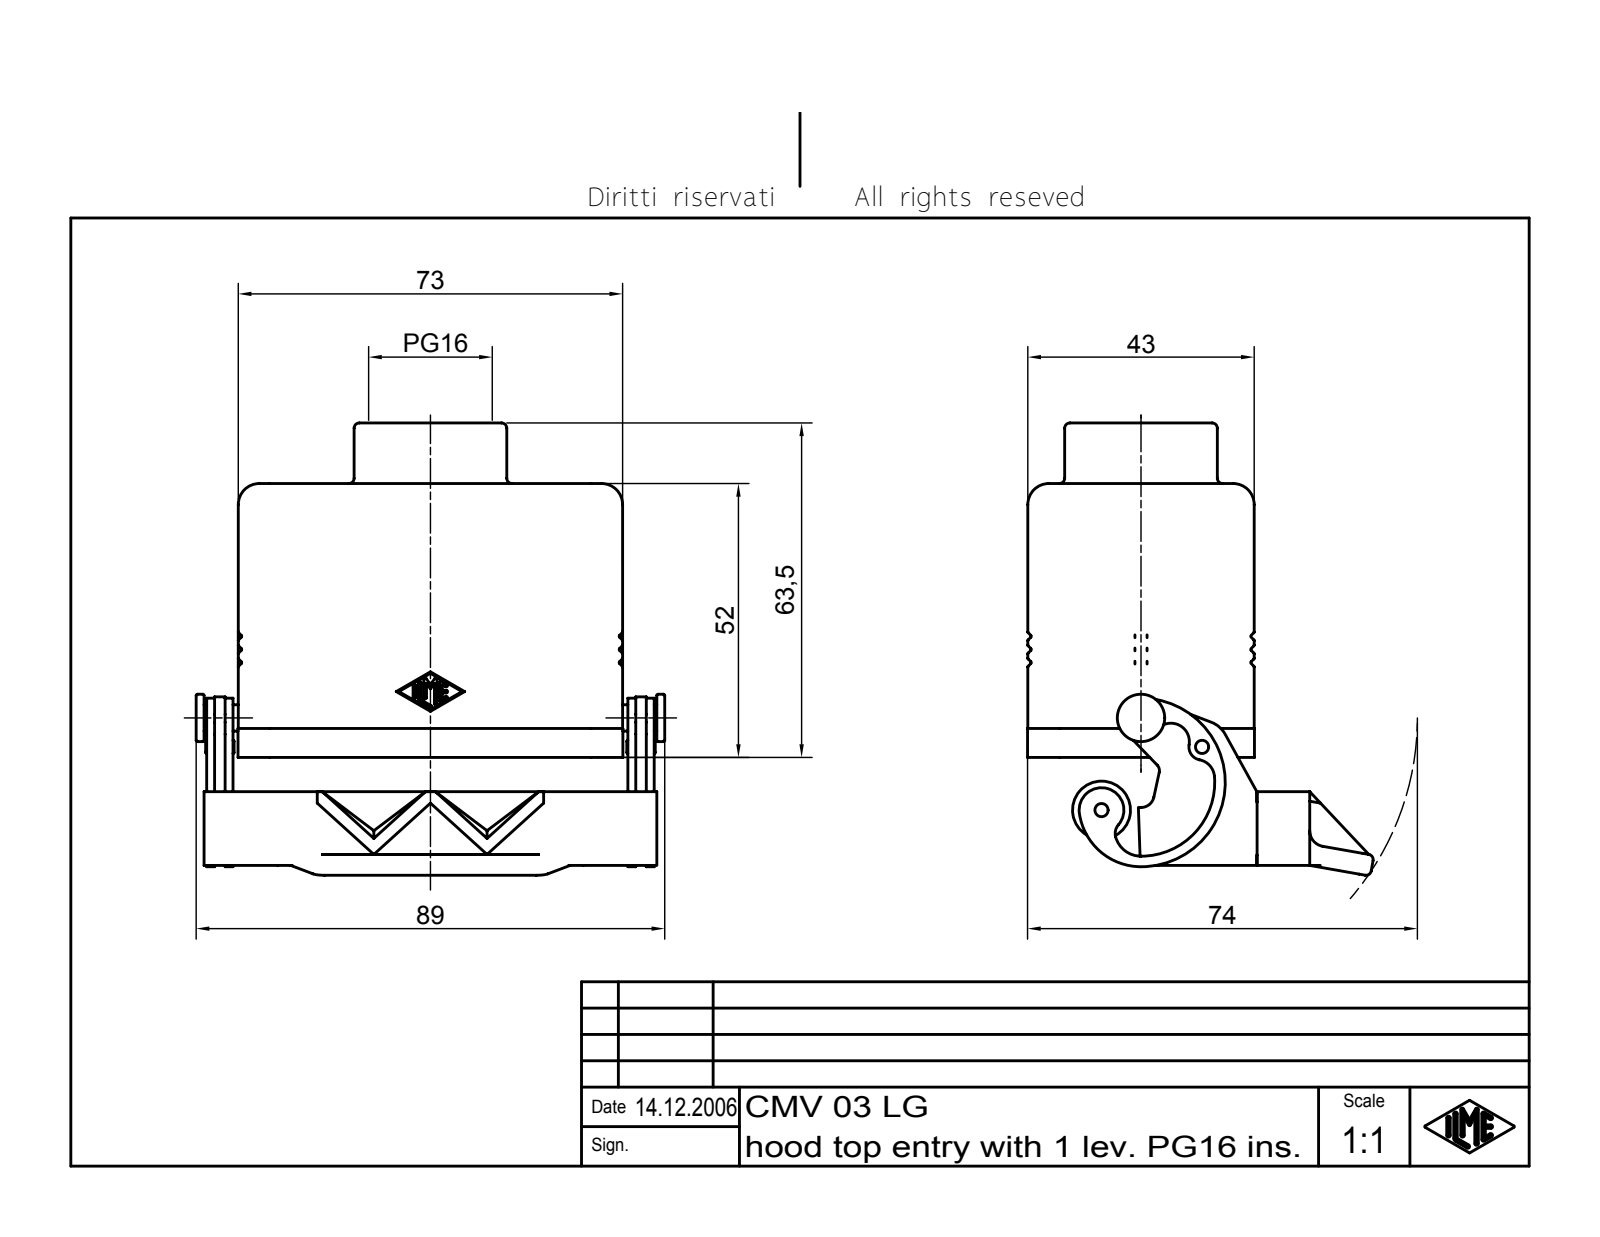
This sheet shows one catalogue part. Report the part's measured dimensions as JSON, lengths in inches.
{"part_name": "CMV 03 LG", "step_written_by": "Autodesk Inventor 7 (AUTOMOTIVE_DESIGN)", "units": "inches", "bodies": {"solids": 1, "faces": 757, "planar": 155, "cylindrical": 279, "other": 323}, "overall_size": [3.504, 3.381, 2.584], "volume_in3": 4.423, "surface_area_in2": 60.55, "round_holes": [[0.098, 1], [0.754, 1], [0.833, 1]], "round_bosses_or_shafts": [[1.142, 1], [0.433, 1], [0.354, 1], [0.197, 1], [0.122, 1], [0.079, 1]], "partial_cylinders_radius": [[0.008, 52], [0.01, 23], [0.098, 9], [0.039, 6], [0.157, 5], [0.096, 4], [0.236, 4], [0.238, 4]], "face_to_face_distances": [0.138, 1.555, 1.693, 0.177, 2.736, 1.417, 0.14, 0.315, 0.453, 2.874]}
